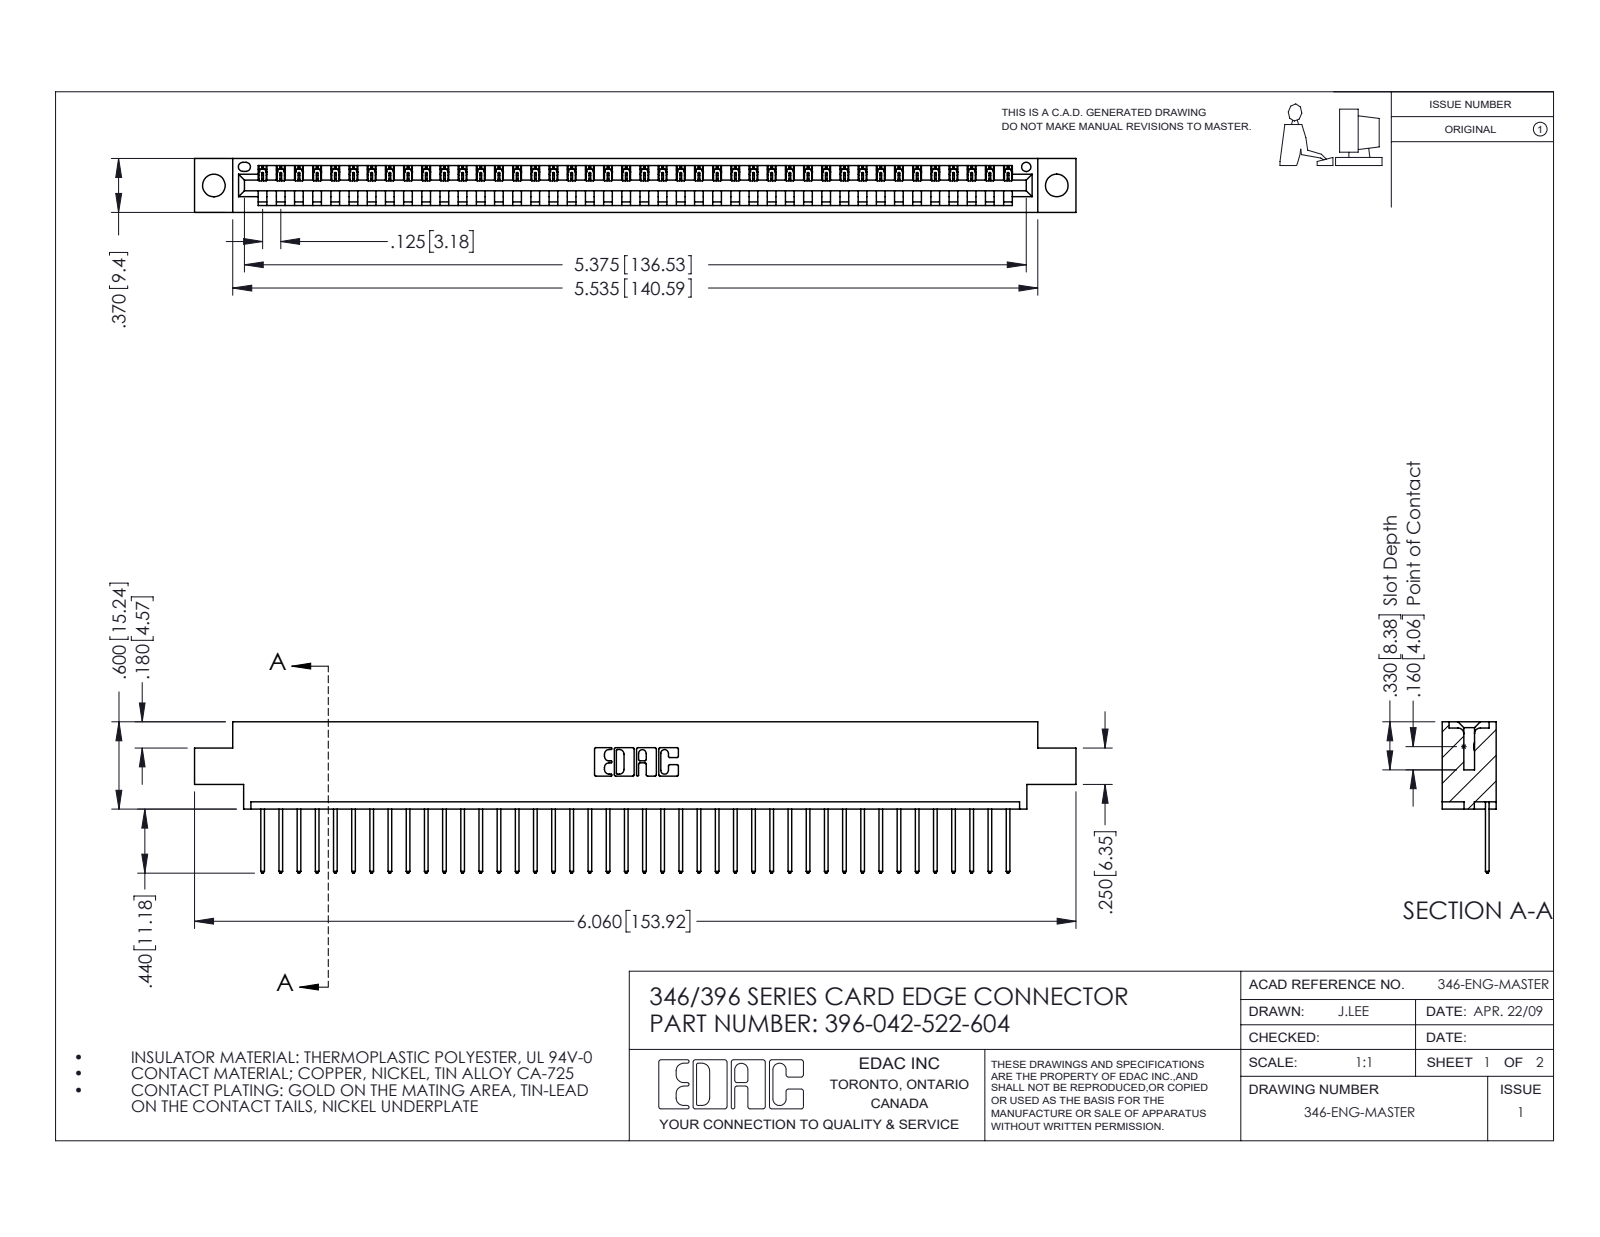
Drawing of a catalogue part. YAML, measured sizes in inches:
part_name: "345-292-001_345-293-122; 346 Part_0.170 Offset - 0.156 Dia-TH; 396-042-522-604"
step_written_by: "SolidWorks 2016 (CONFIG_CONTROL_DESIGN)"
units: inches
bodies: {solids: 43, faces: 2562, planar: 1760, cylindrical: 802, other: 0}
overall_size: [6.06, 1.04, 0.37]
volume: 0.885
surface_area: 28.27
round_holes:
  - {diameter: 0.156, count: 2}
  - {diameter: 0.064, count: 1}
partial_cylinders:
  - {radius: 0.006, count: 84}
  - {radius: 0.01, count: 84}
  - {radius: 0.01, count: 22}
  - {radius: 0.007, count: 6}
  - {radius: 0.031, count: 6}
  - {radius: 0.026, count: 3}
  - {radius: 0.031, count: 2}
  - {radius: 0.04, count: 2}
face_to_face_distances: [0.048, 0.322, 0.37, 0.25, 0.072, 0.298, 0.025, 0.148, 0.222, 0.1]
hole_center_spacings: [0.246, 5.586, 5.795]
